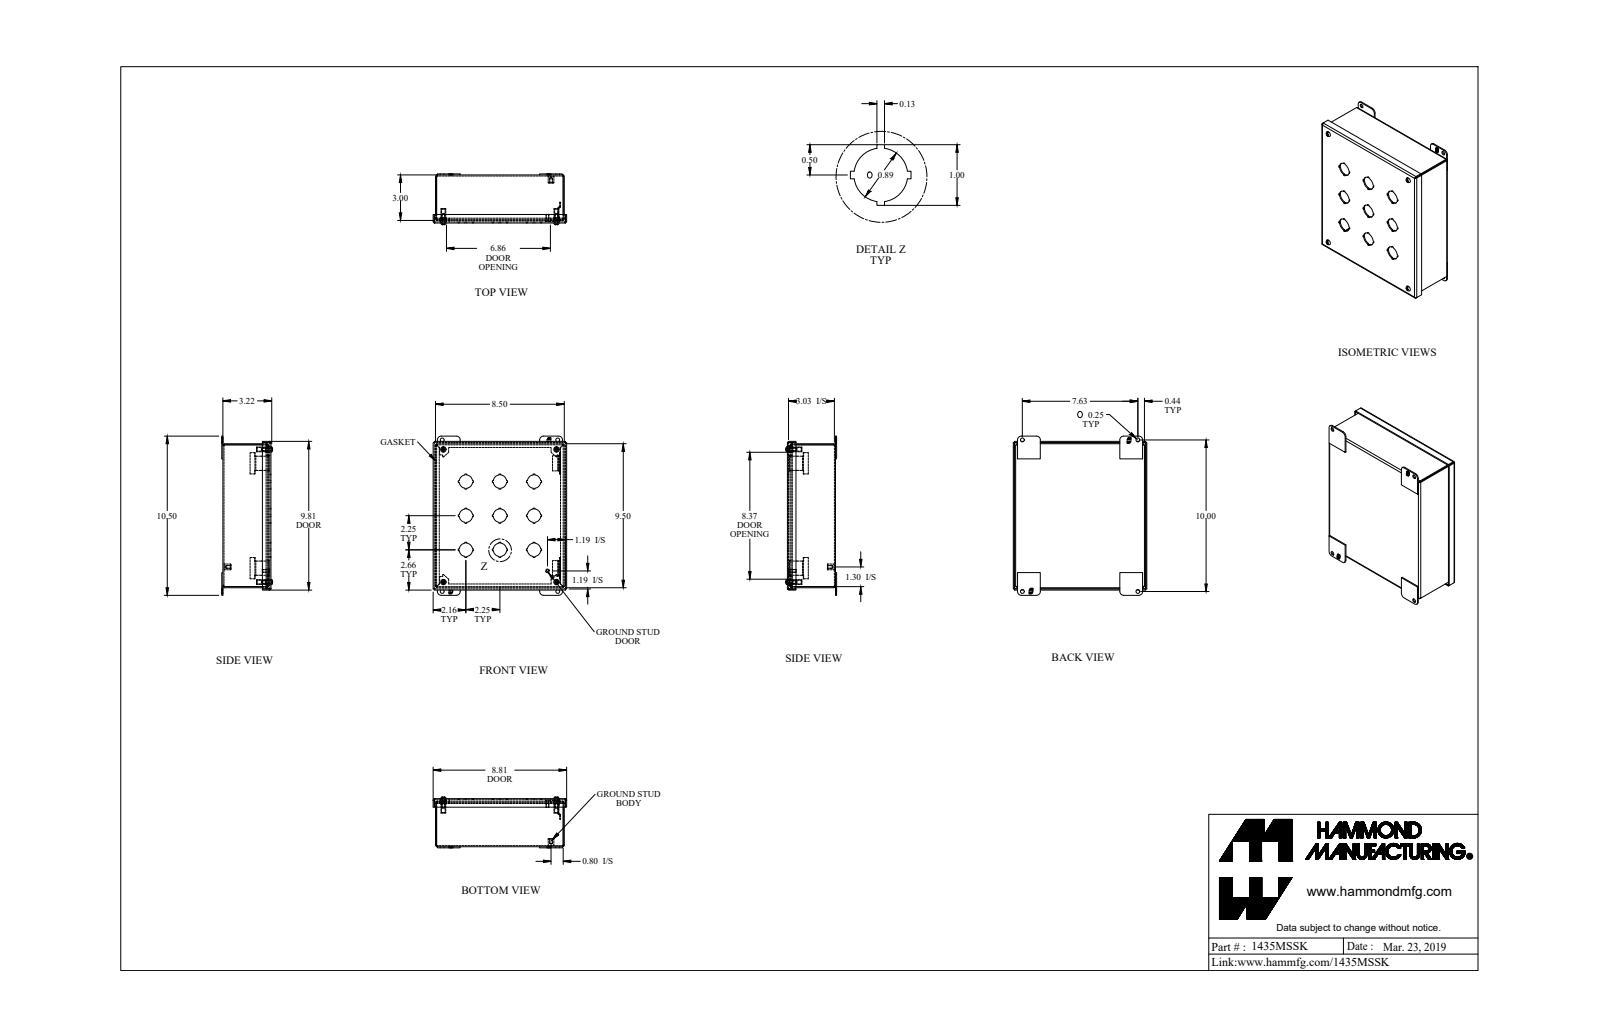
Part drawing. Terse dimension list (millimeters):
name: 1435MSSK_Default
written by: SolidWorks 2019 (CONFIG_CONTROL_DESIGN)
unit: mm
bodies: 23 solids, 749 faces (531 planar, 188 cylindrical, 30 other)
size: 266.7 × 223.8 × 85.2
volume: 412 500 mm³; area: 431 000 mm²
holes: 9× ⌀22.5, 8× ⌀6.4, 4× ⌀1.7, 4× ⌀6.1, 4× ⌀6.4, 4× ⌀10.3, 1× ⌀4
bosses: 5× ⌀4.8, 4× ⌀10.3, 4× ⌀8, 4× ⌀3.8, 1× ⌀9.5, 1× ⌀6.4
rounds: 12× R0.9, 12× R2.7, 8× R6.4, 4× R0.7, 4× R2.2, 4× R4.3
face distances: 1.8, 78.7, 80.6, 76.9, 214.1, 239.5, 3.9, 215.9, 212.2, 241.3
hole spacings: 57.2, 80.8, 127.8, 189.5, 189.5, 192.3, 222.2, 222.3
